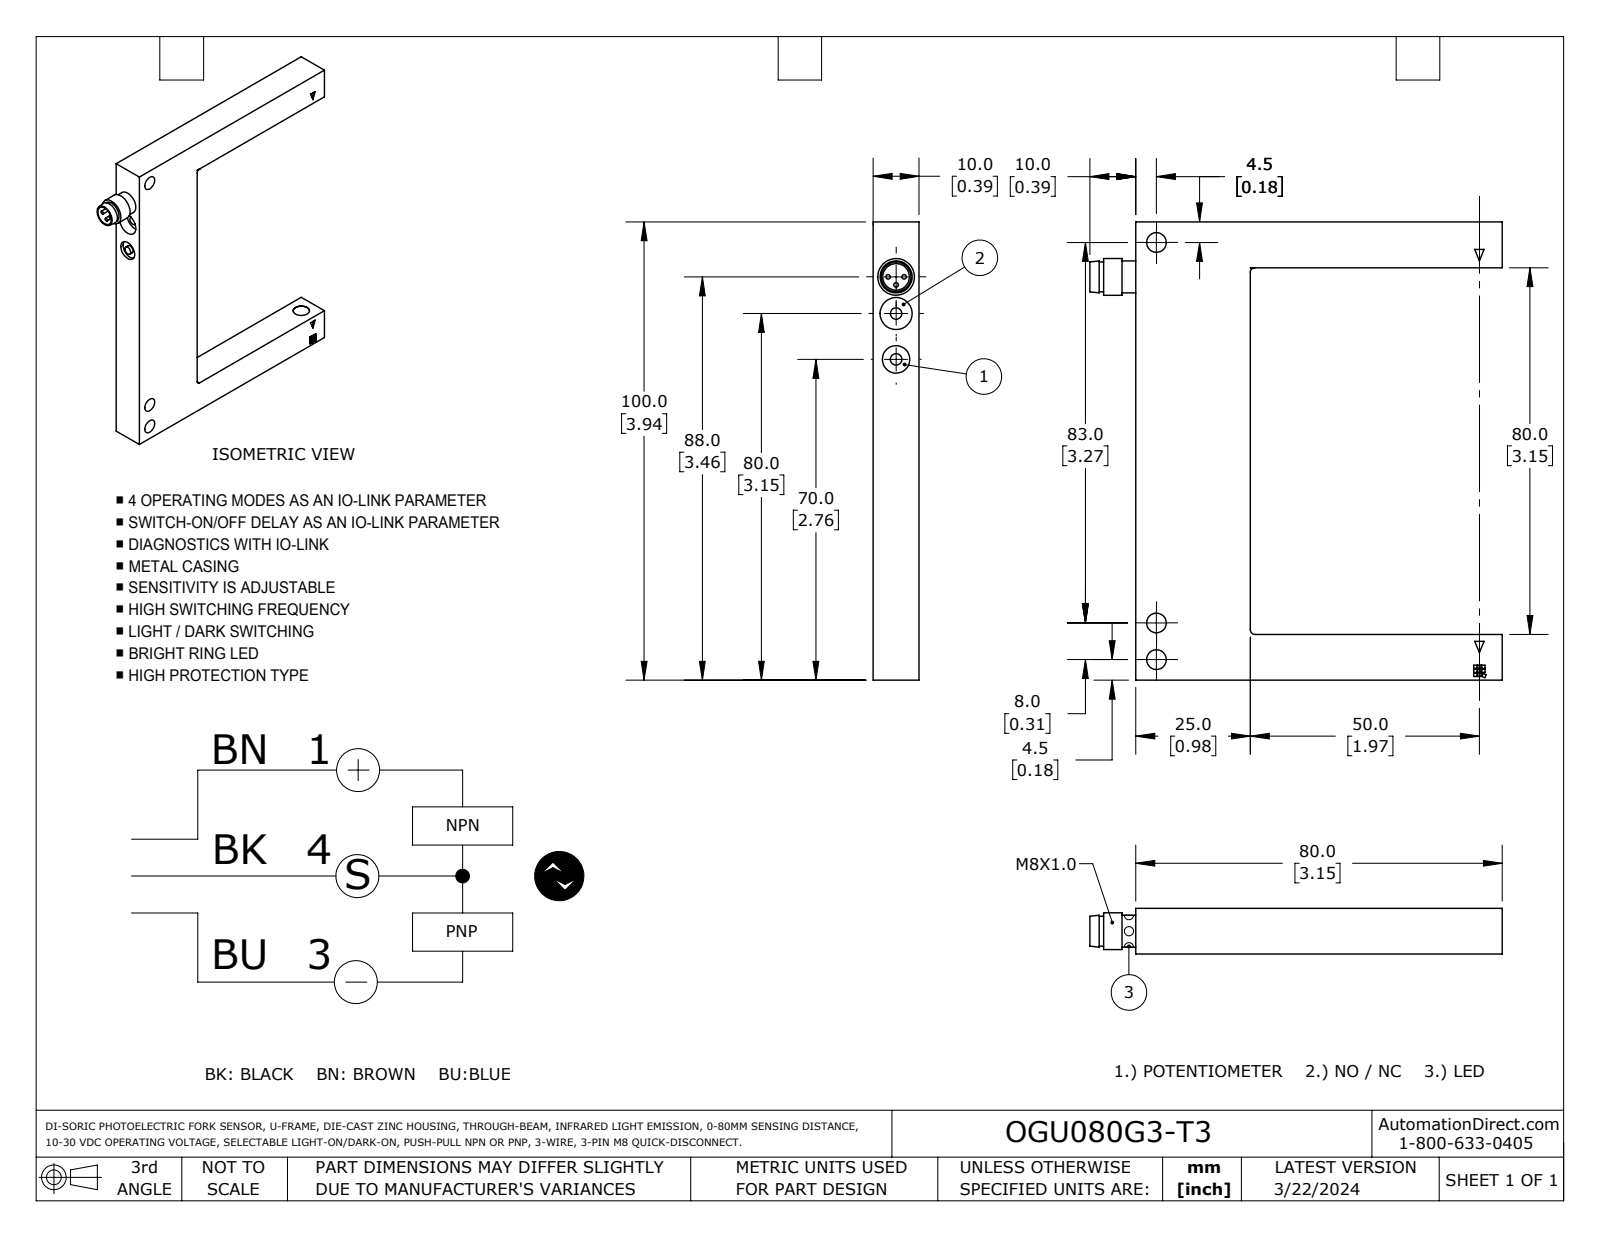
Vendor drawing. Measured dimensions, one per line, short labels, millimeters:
name: OGU080G3-T3
written by: SolidWorks 2023 (AUTOMOTIVE_DESIGN)
unit: mm
bodies: 1 solid, 112 faces (91 planar, 20 cylindrical, 1 other)
size: 100 × 90 × 10
volume: 35 710 mm³; area: 12 750 mm²
holes: 3× ⌀4.3, 1× ⌀3, 1× ⌀5, 1× ⌀5.8, 1× ⌀6, 1× ⌀7
bosses: 3× ⌀1, 2× ⌀2.5, 1× ⌀8, 1× ⌀7, 1× ⌀6.5
rounds: 3× R1
face distances: 10, 90, 100, 25, 80, 55, 10, 1, 90, 80.1
hole spacings: 8, 10, 18, 83, 91
